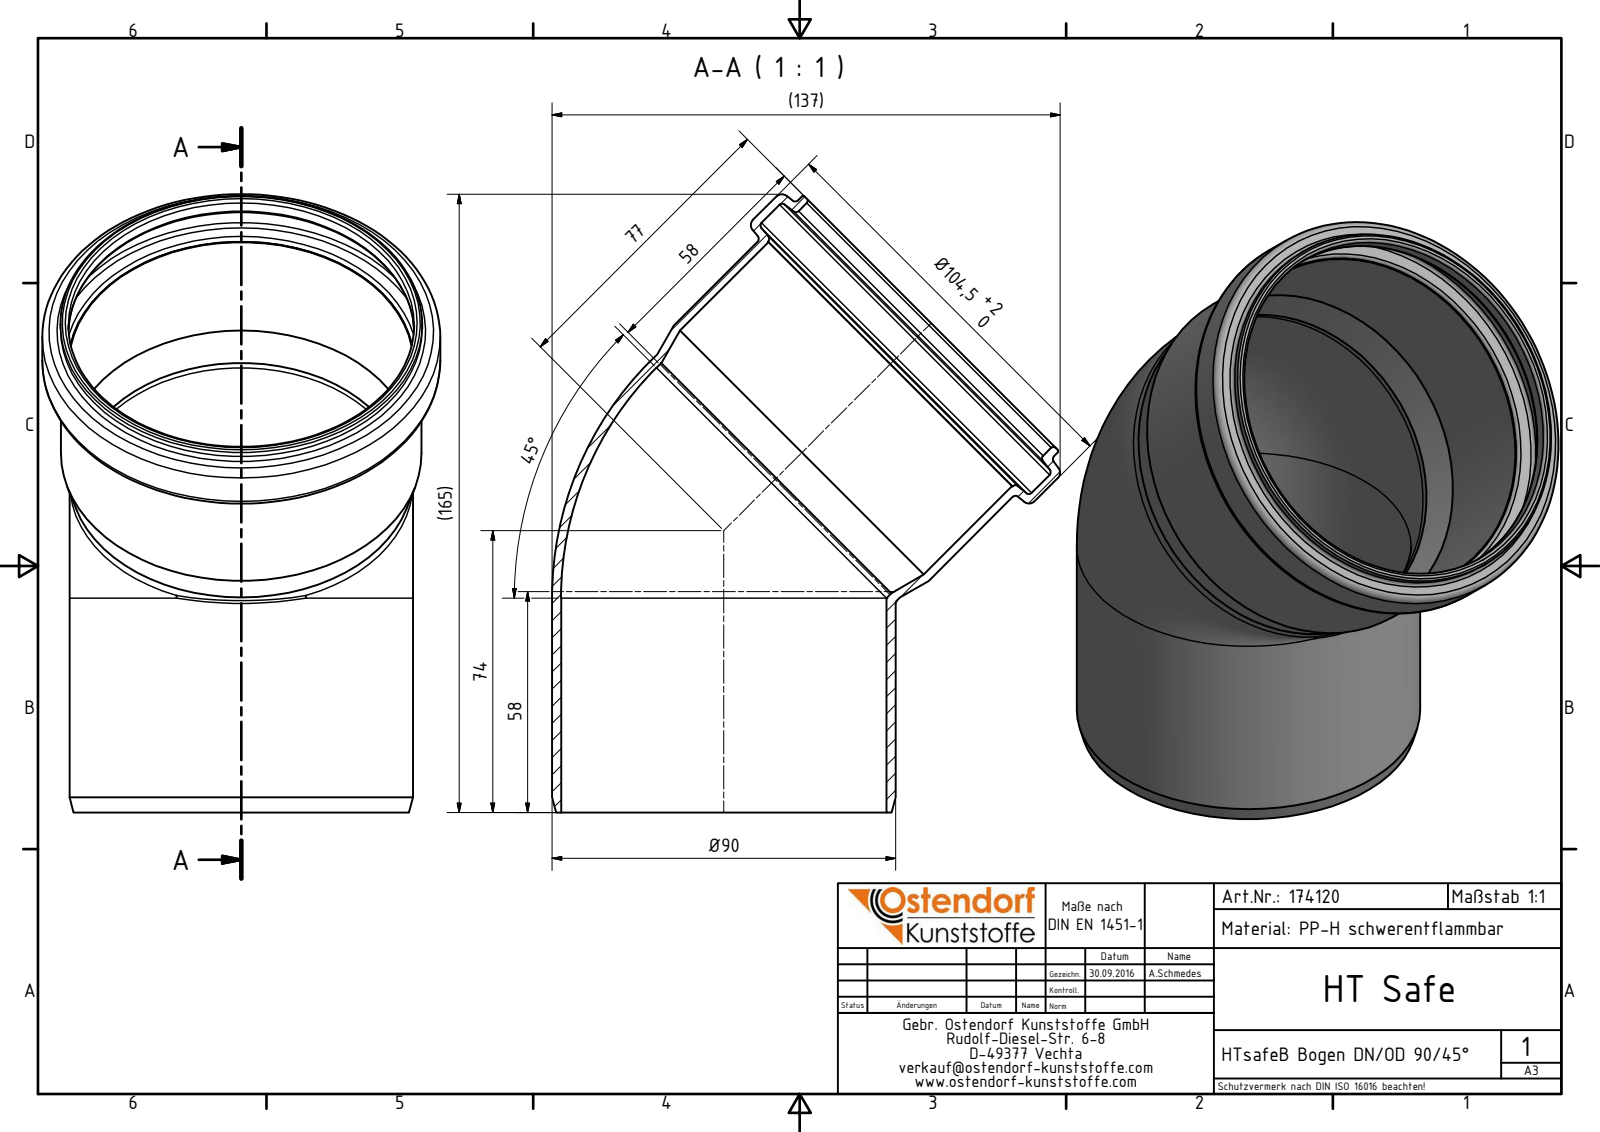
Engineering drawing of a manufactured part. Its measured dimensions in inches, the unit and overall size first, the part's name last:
Units: inches
Overall size (bounding box): 6.39 × 5.252 × 4.114
Round holes (diameter × count): ⌀3.364 ×2, ⌀3.575 ×2, ⌀3.563 ×1, ⌀3.949 ×1
Round bosses / shafts (diameter × count): ⌀3.551 ×2, ⌀4.114 ×1, ⌀3.74 ×1, ⌀3.728 ×1
Main face-to-face distances: 0.599, 1.665, 2.264
Volume: 5.747 in³ · Surface area: 139.4 in²
Bodies: 1 solid, 35 faces (4 planar, 11 cylindrical, 20 other)
Part name (STEP PRODUCT): 174120 HTsafeB DN_OD 90_45°
STEP written by: Autodesk Inventor 2016 (AUTOMOTIVE_DESIGN)
